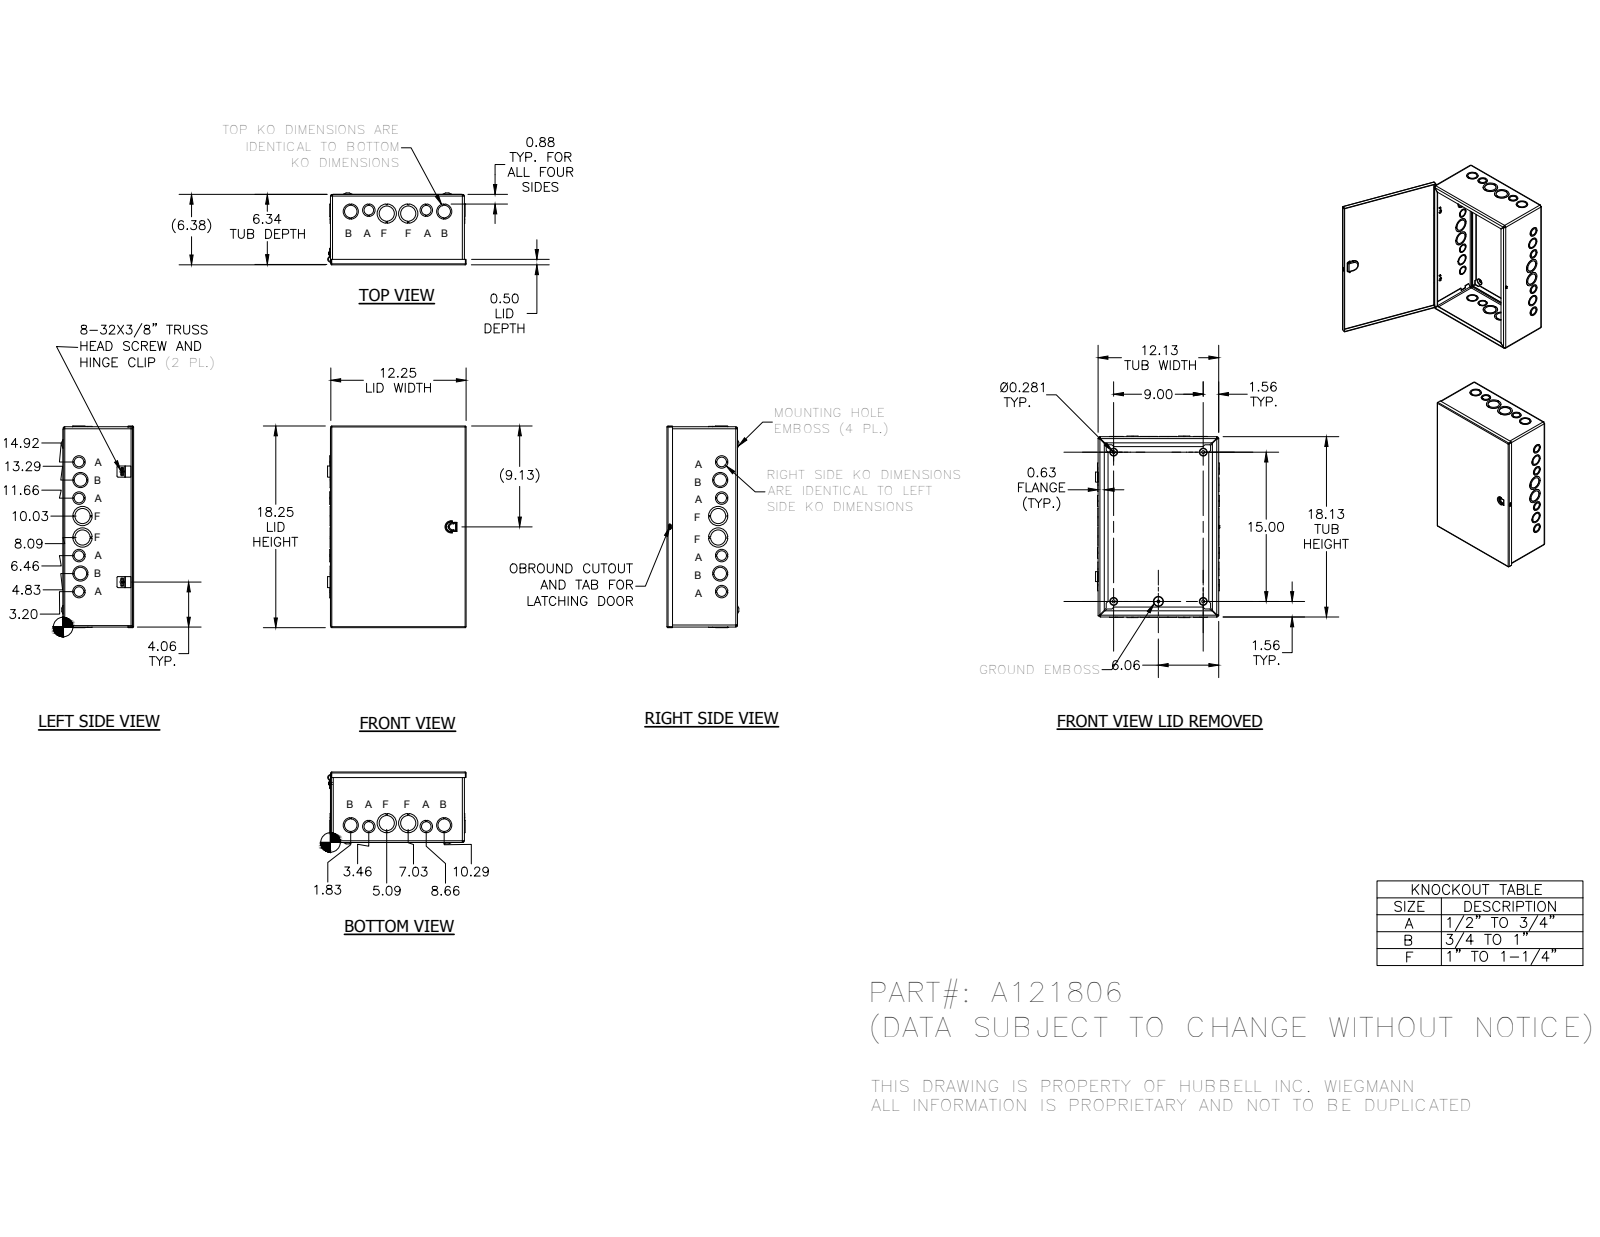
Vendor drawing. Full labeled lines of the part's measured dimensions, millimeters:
Part name (STEP PRODUCT): A1218BA; A121806WRA; 31816; 372177 (+3 more)
STEP written by: Autodesk Inventor 2014 (AUTOMOTIVE_DESIGN)
Units: millimetres
Bodies: 31 solids, 1279 faces (846 planar, 275 cylindrical, 158 other)
Overall size (bounding box): 468.29 × 320.97 × 165.19
Round holes (diameter × count): ⌀28.57 ×10, ⌀34.92 ×8, ⌀22.22 ×6, ⌀7.62 ×4, ⌀44.45 ×4, ⌀3.56 ×2, ⌀4.19 ×1
Round bosses / shafts (diameter × count): ⌀9.75 ×2, ⌀4.17 ×2, ⌀5.8 ×1
Partial cylindrical surfaces — rounded edges, fillets, slot ends (radius × count): R3.17 ×15, R0.79 ×10, R1.59 ×9, R2.38 ×8, R4.75 ×8, R1.4 ×4, R1.57 ×4, R1.78 ×4
Main face-to-face distances: 1.58, 1.57, 160.43, 158.85, 1.59, 160.44, 162.02, 307.98, 306.4, 306.41
Hole centre spacings: 41.52, 42.15, 82.94, 91.03, 132.17, 173.51, 214.88, 49.28
